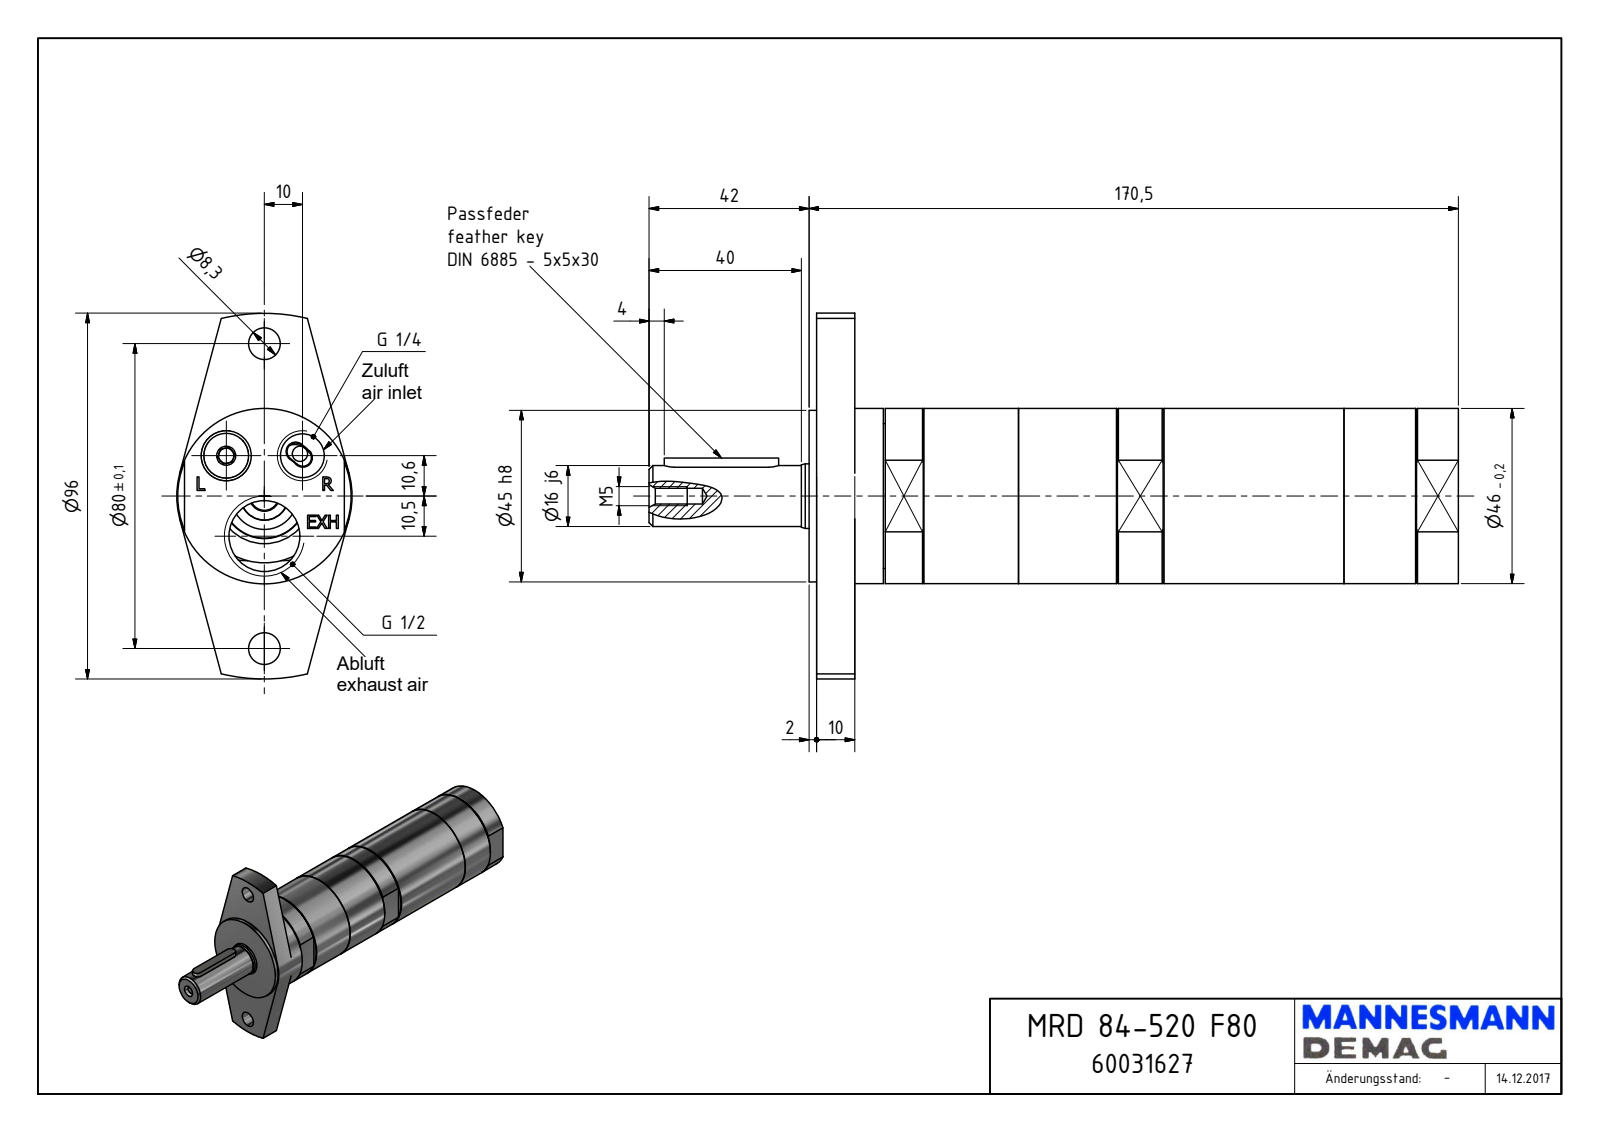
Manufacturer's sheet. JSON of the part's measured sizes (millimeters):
{"part_name": "MRD 84-520 F80_60031627", "step_written_by": "Autodesk Inventor 2018 (AUTOMOTIVE_DESIGN)", "units": "millimeters", "bodies": {"solids": 1, "faces": 186, "planar": 115, "cylindrical": 41, "other": 30}, "overall_size": [212.5, 96, 46], "volume_mm3": 300995, "surface_area_mm2": 38333, "round_holes": [[8.3, 2], [4, 1], [4.13, 1], [11.45, 1], [17.5, 1], [18.63, 1], [38, 1], [38.38, 1]], "round_bosses_or_shafts": [[46, 1], [45, 1], [33.29, 1], [16.95, 1], [16, 1]], "partial_cylinders_radius": [[2.5, 6], [5, 2], [5.72, 1], [16.75, 1], [48, 1]], "face_to_face_distances": [10, 2, 12, 158.5, 170.5, 168.5, 42, 8, 150.5, 18], "hole_center_spacings": [14.57, 23.35, 31.05, 40, 51.58, 10.5, 20, 29.5]}
